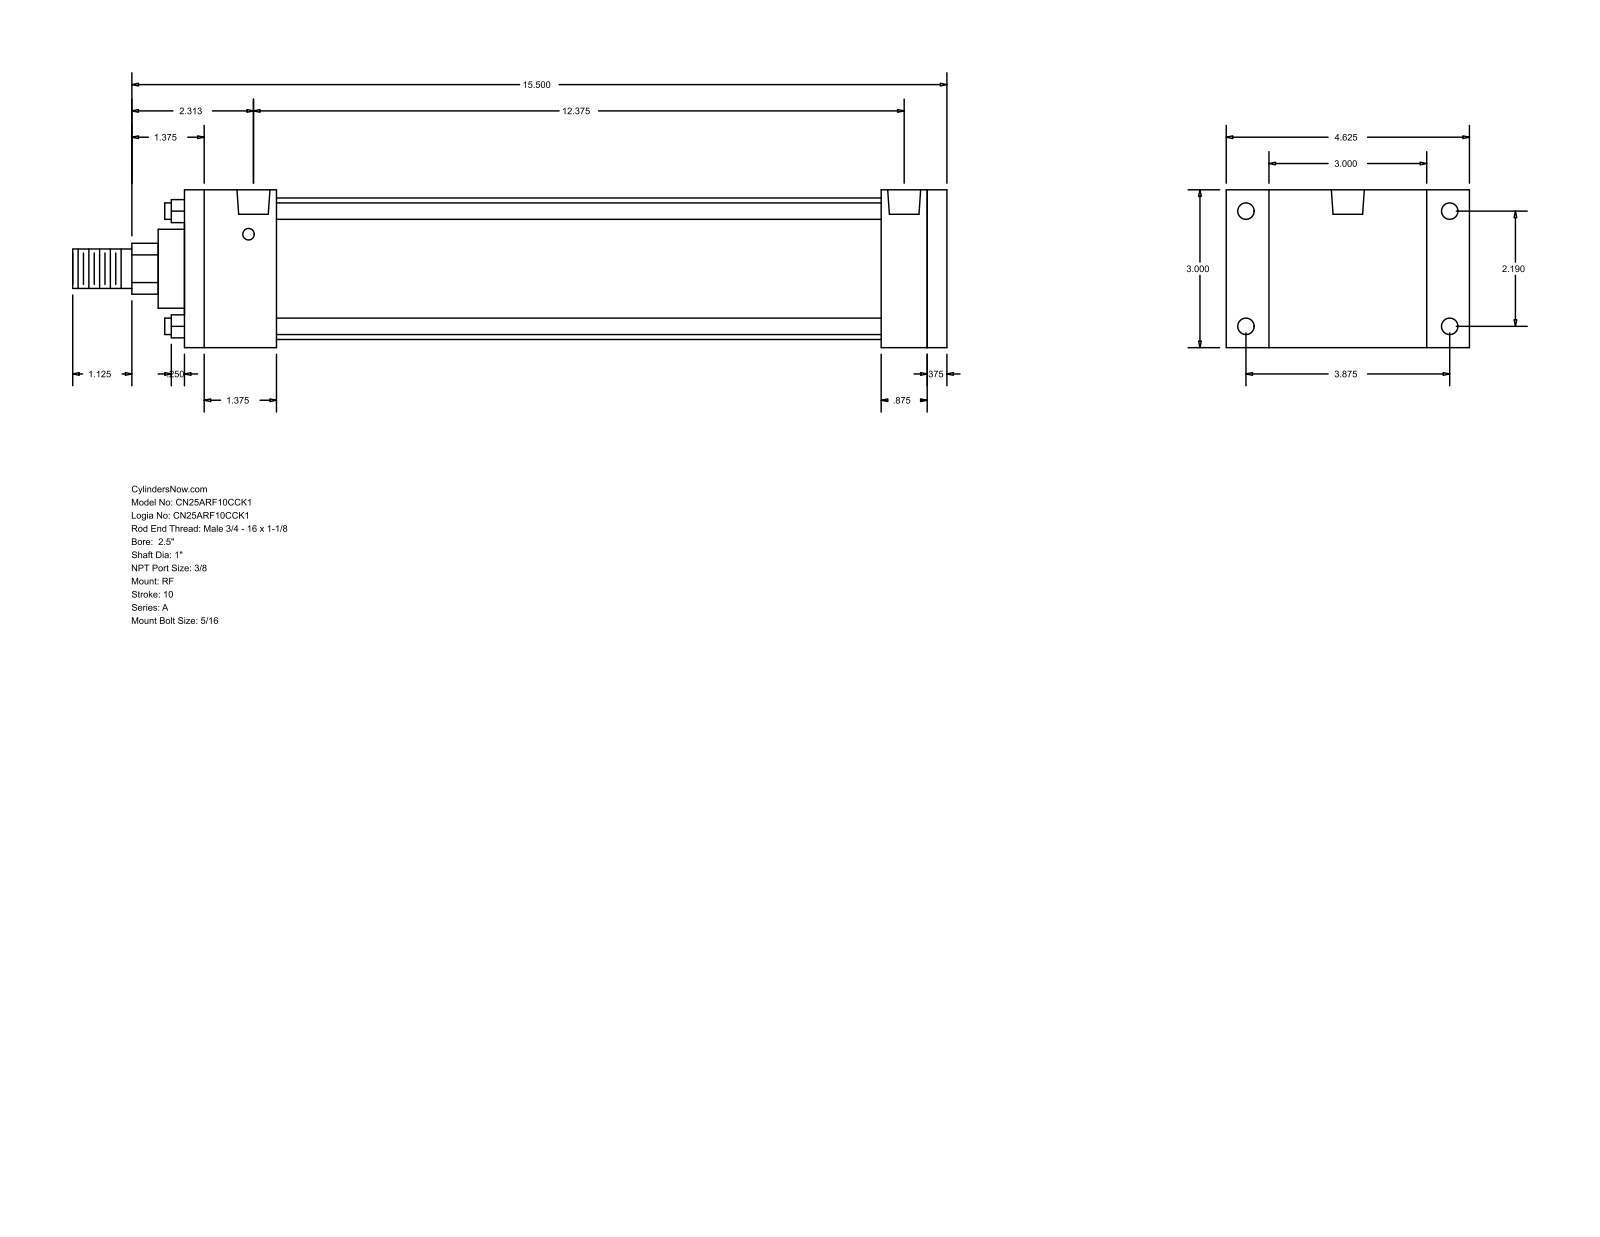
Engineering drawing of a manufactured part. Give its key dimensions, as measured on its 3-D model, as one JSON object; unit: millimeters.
{"part_name": "A_RF__0250_1", "step_written_by": "GSSL Pune (CONFIG_CONTROL_DESIGN)", "units": "millimeters", "bodies": {"solids": 0, "faces": 92, "planar": 64, "cylindrical": 28, "other": 0}, "overall_size": [422.27, 117.47, 76.2], "round_holes": [[5.56, 4], [7.94, 4], [15.93, 2]], "round_bosses_or_shafts": [[7.94, 4], [68.33, 1], [38.1, 1], [25.4, 1], [19.05, 1]], "partial_cylinders_radius": [[12.29, 1]], "face_to_face_distances": [76.2, 368.3, 9.52, 358.78, 44.45, 336.55, 292.1, 314.33, 323.85, 22.23], "hole_center_spacings": [2.38, 55.62, 98.42, 113.05, 316.7, 319.08, 314.32]}
